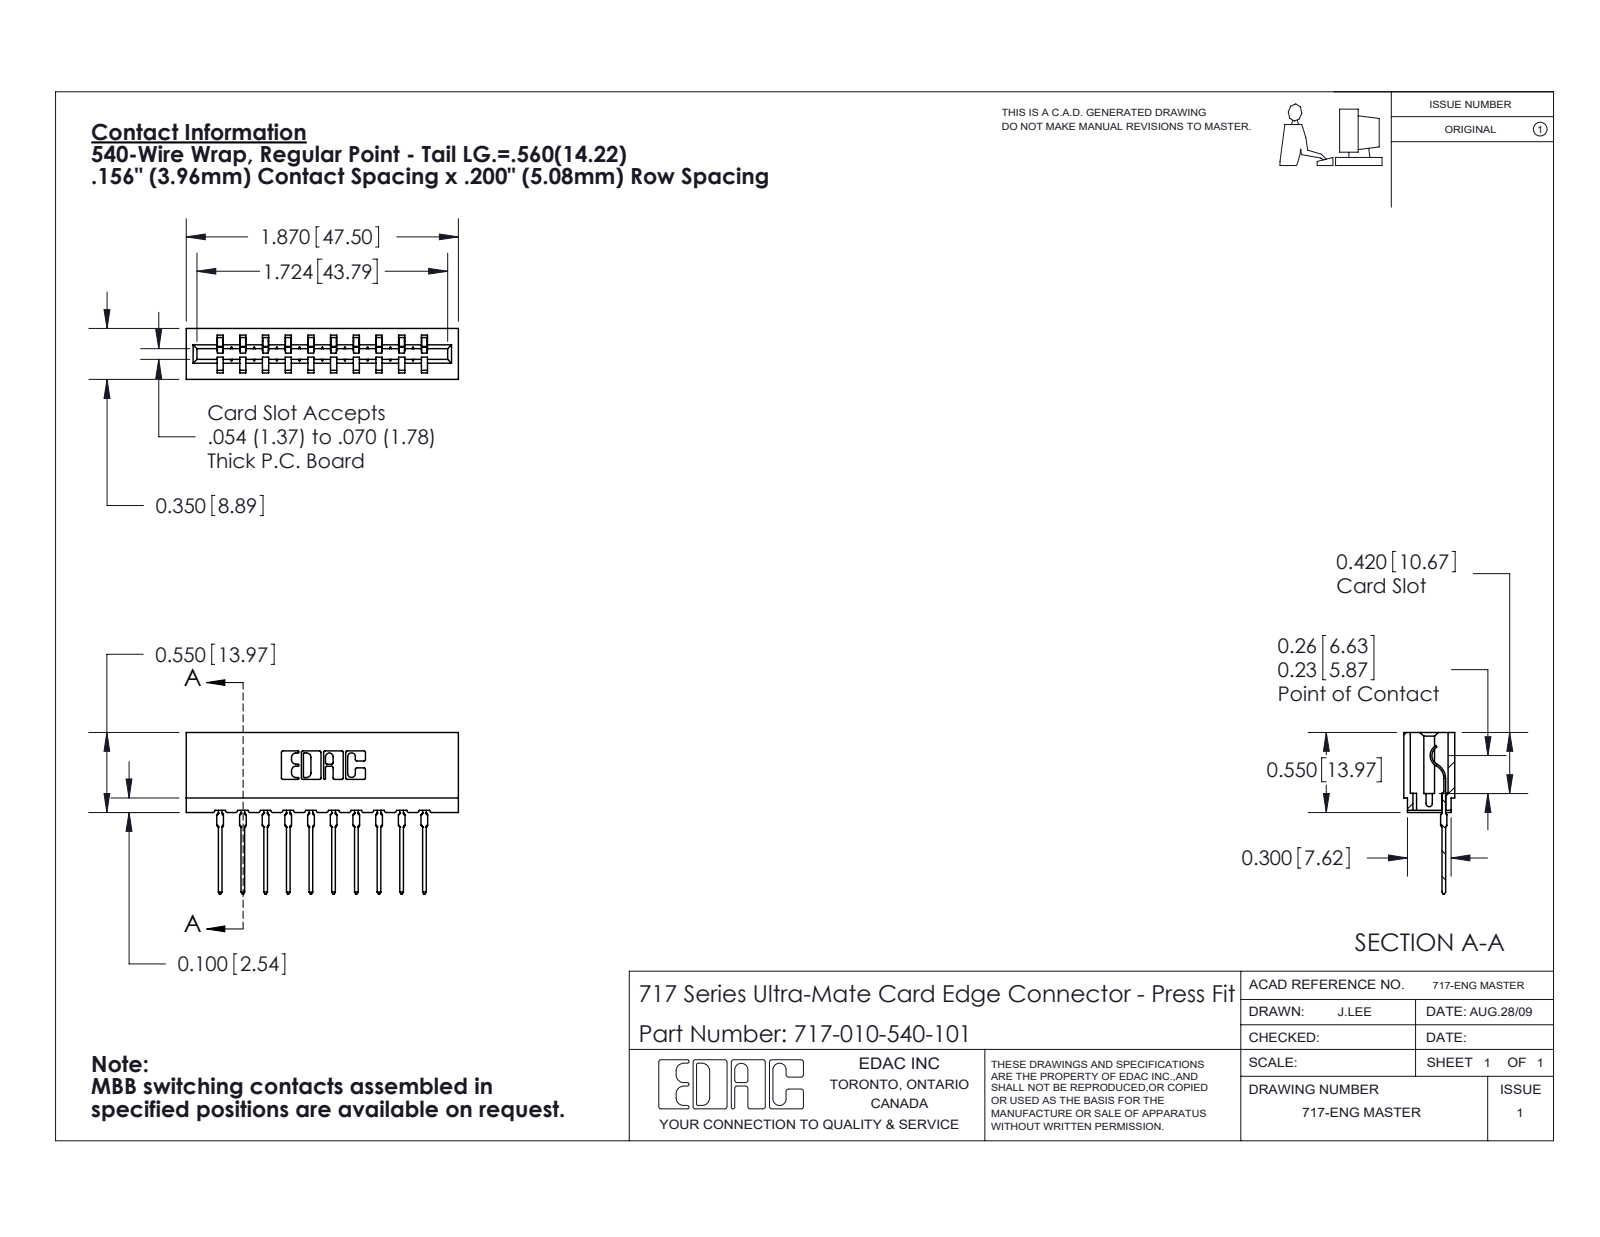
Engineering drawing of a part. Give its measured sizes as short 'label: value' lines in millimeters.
name: 717 Part_Insulator Option - 06; 745-292-001_540; 717-010-540-101
written by: SolidWorks 2020 (CONFIG_CONTROL_DESIGN)
unit: mm
bodies: 11 solids, 1224 faces (734 planar, 230 cylindrical, 260 other)
size: 47.5 × 28.2 × 8.9
volume: 4 180 mm³; area: 5 638 mm²
rounds: 22× R0.3, 20× R0.4, 20× R0.5, 6× R0.2, 6× R0.8, 4× R0.1, 4× R0.3, 3× R0.7
face distances: 4, 5.4, 3.5, 15.8, 8.9, 11.9, 5, 7.9, 9, 7.9
